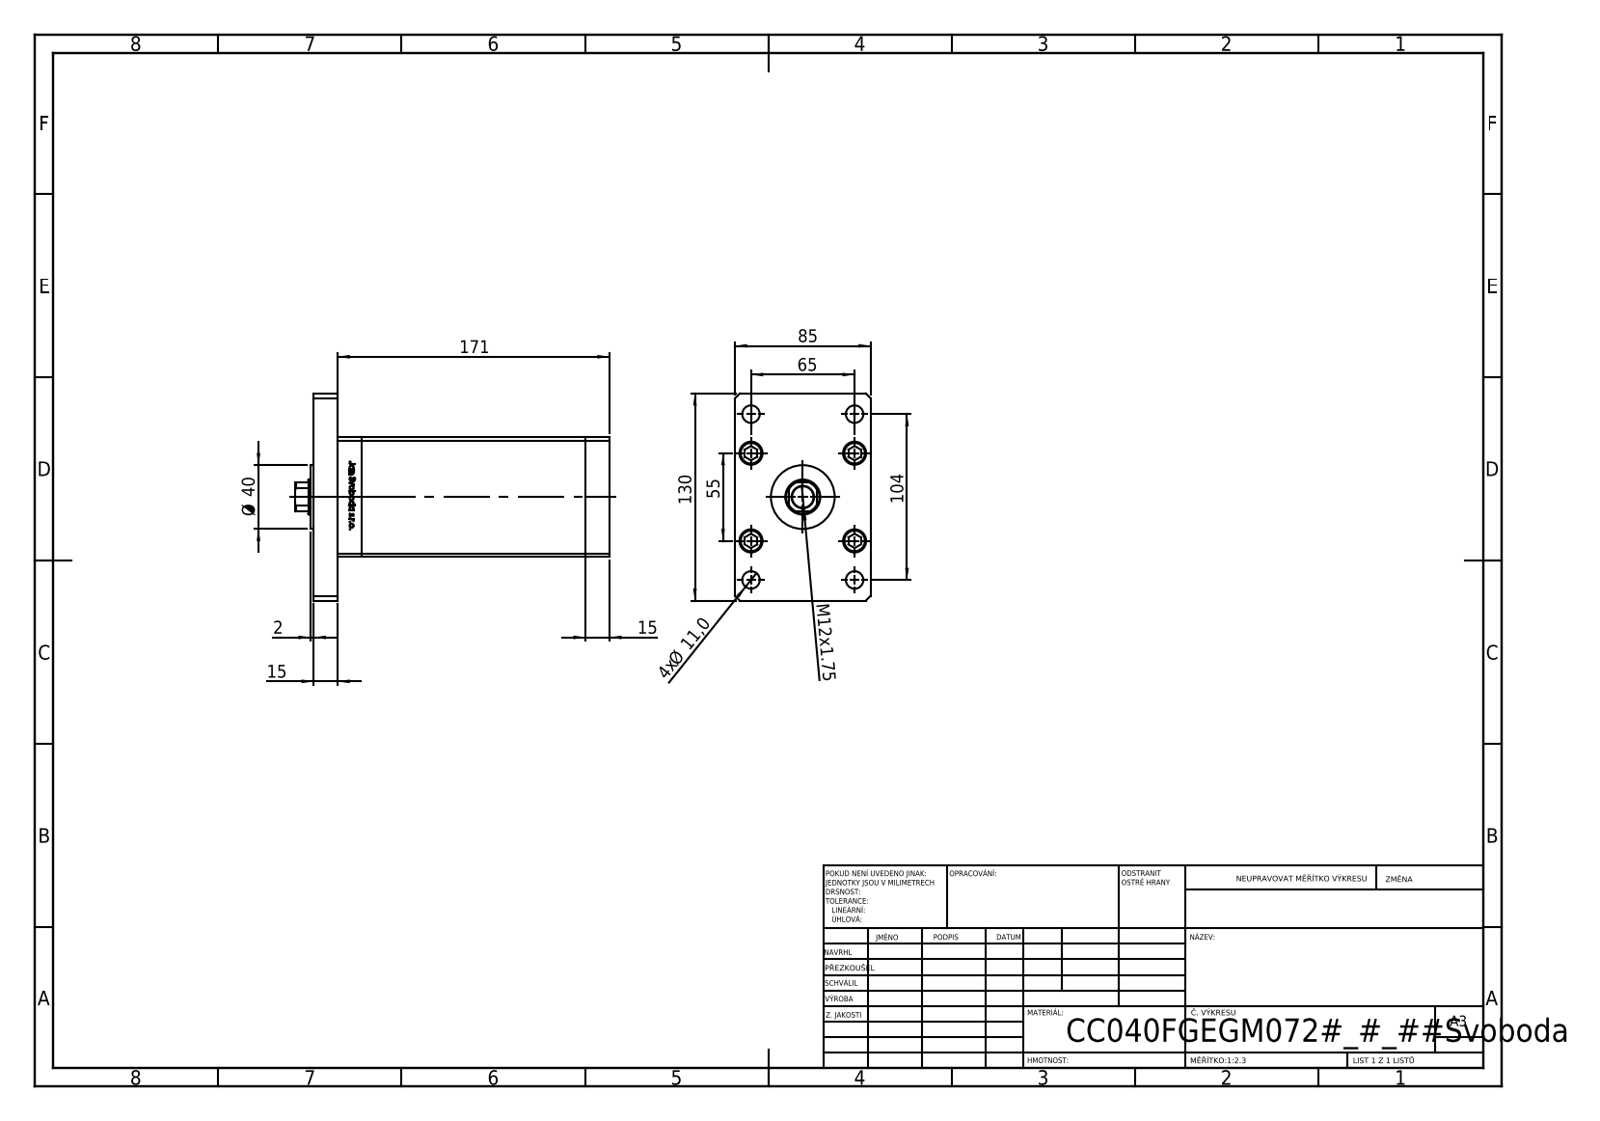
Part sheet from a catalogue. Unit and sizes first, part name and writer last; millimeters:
Units: millimetres
Overall size (bounding box): 197 × 130 × 85
Round holes (diameter × count): ⌀11 ×9, ⌀15.5 ×5, ⌀10 ×4, ⌀14.5 ×4, ⌀2 ×2, ⌀13.16 ×2, ⌀13.5 ×1, ⌀22 ×1, ⌀23.5 ×1
Round bosses / shafts (diameter × count): ⌀8 ×9, ⌀14.5 ×5, ⌀40 ×1
Partial cylindrical surfaces — rounded edges, fillets, slot ends (radius × count): R0.93 ×2, R10.5 ×1
Main face-to-face distances: 15, 85, 155.5, 170.5, 75, 30, 140.5, 185.5, 10.5, 27.5
Hole centre spacings: 28, 24.5, 42.57, 61.32, 65, 69.46, 79.5, 102.69
Volume: 1 123 000 mm³ · Surface area: 194 613 mm²
Bodies: 19 solids, 1310 faces (517 planar, 187 cylindrical, 606 other)
Part name (STEP PRODUCT): V220C_F; V220C_FRONT_F; V220C_VC_F; ALLEN BOLT (+2 more)
STEP written by: SolidWorks 2019 (CONFIG_CONTROL_DESIGN)
